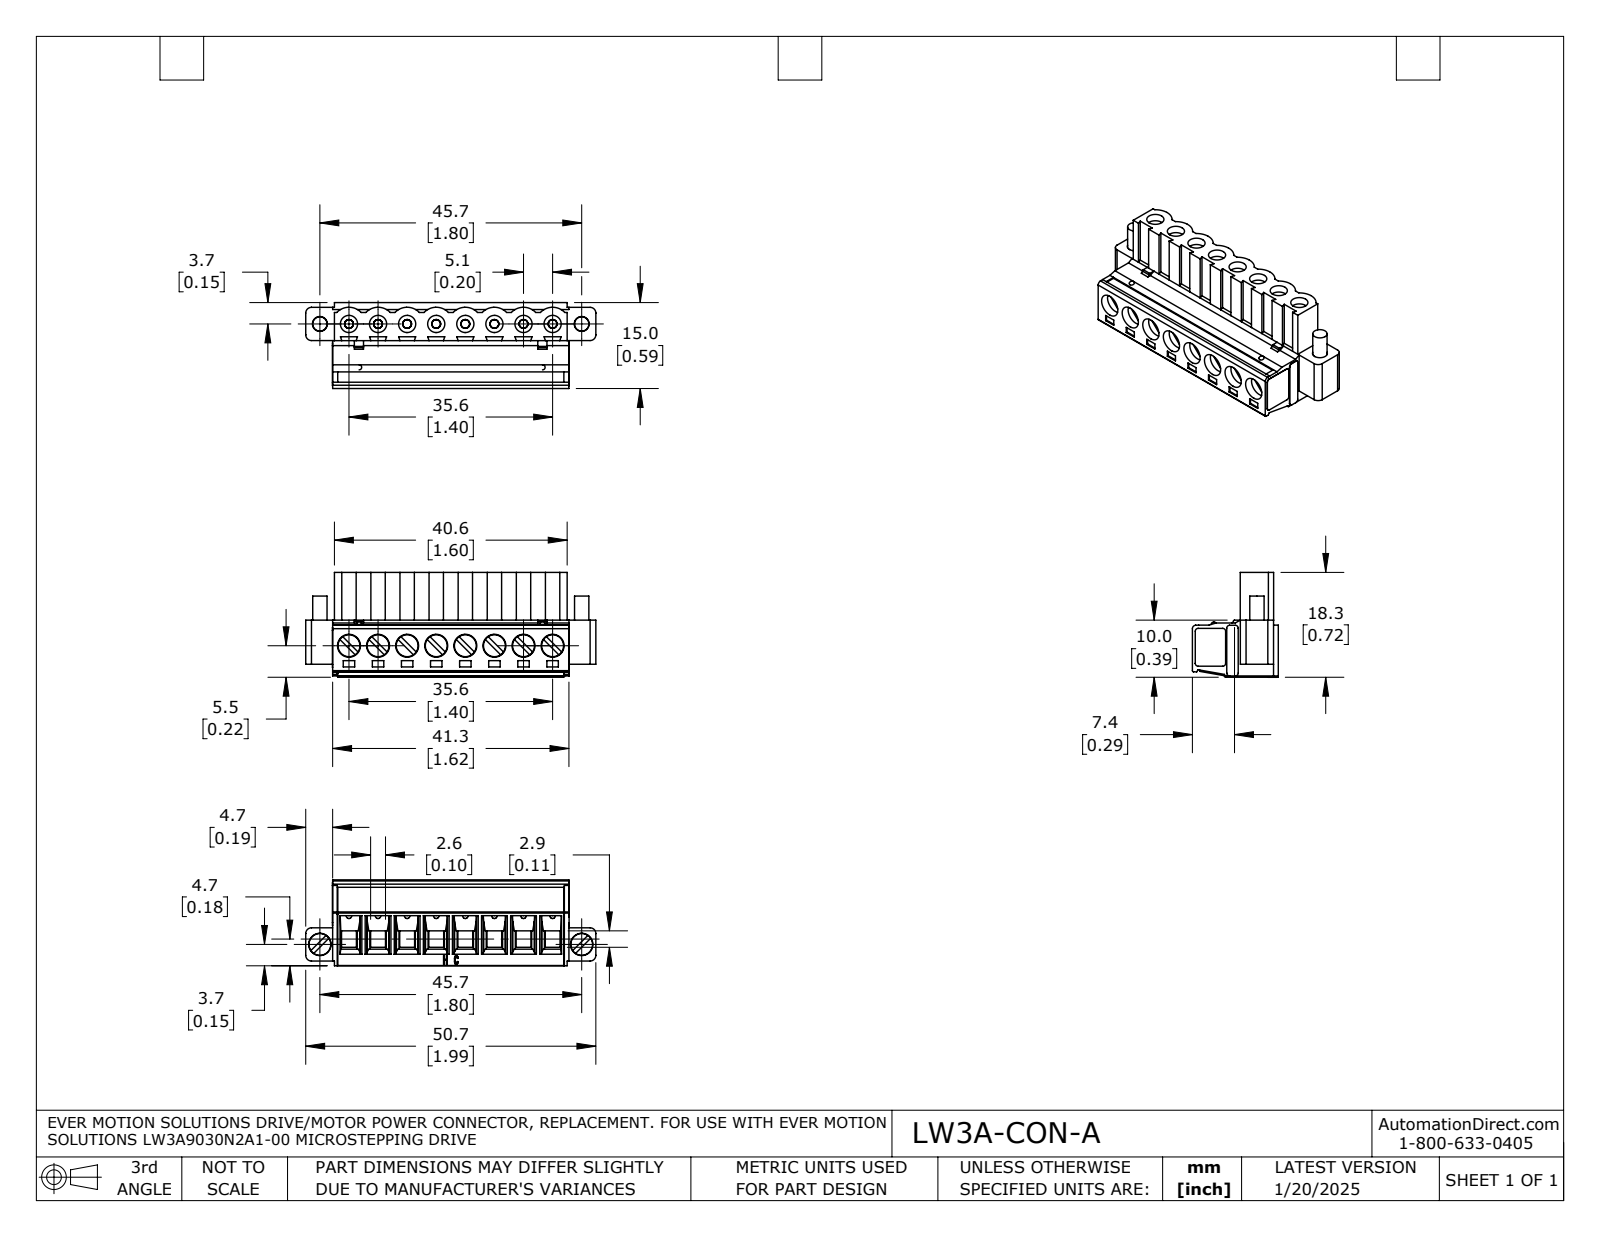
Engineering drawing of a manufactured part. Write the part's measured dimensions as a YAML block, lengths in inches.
part_name: "LW3A-CON-A"
step_written_by: "SolidWorks 2021 (AUTOMOTIVE_DESIGN)"
units: inches
bodies: {solids: 27, faces: 1444, planar: 1179, cylindrical: 229, other: 36}
overall_size: [1.994, 0.721, 0.591]
volume: 0.39
surface_area: 14.04
round_holes:
  - {diameter: 0.118, count: 16}
  - {diameter: 0.059, count: 8}
  - {diameter: 0.06, count: 8}
  - {diameter: 0.157, count: 8}
  - {diameter: 0.102, count: 2}
  - {diameter: 0.154, count: 2}
round_bosses_or_shafts:
  - {diameter: 0.15, count: 8}
  - {diameter: 0.06, count: 8}
  - {diameter: 0.15, count: 2}
  - {diameter: 0.098, count: 2}
  - {diameter: 0.015, count: 1}
partial_cylinders:
  - {radius: 0.012, count: 15}
  - {radius: 0.02, count: 12}
  - {radius: 0.005, count: 10}
  - {radius: 0.115, count: 8}
  - {radius: 0.008, count: 5}
  - {radius: 0.007, count: 4}
  - {radius: 0.039, count: 4}
  - {radius: 0.015, count: 1}
face_to_face_distances: [0.2, 0.4, 0.6, 0.15, 0.8, 0.35, 0.05, 1, 0.55, 0.25]
hole_center_spacings: [0.2, 0.4, 0.6, 0.8, 1, 0.2, 0.2, 1.2]
